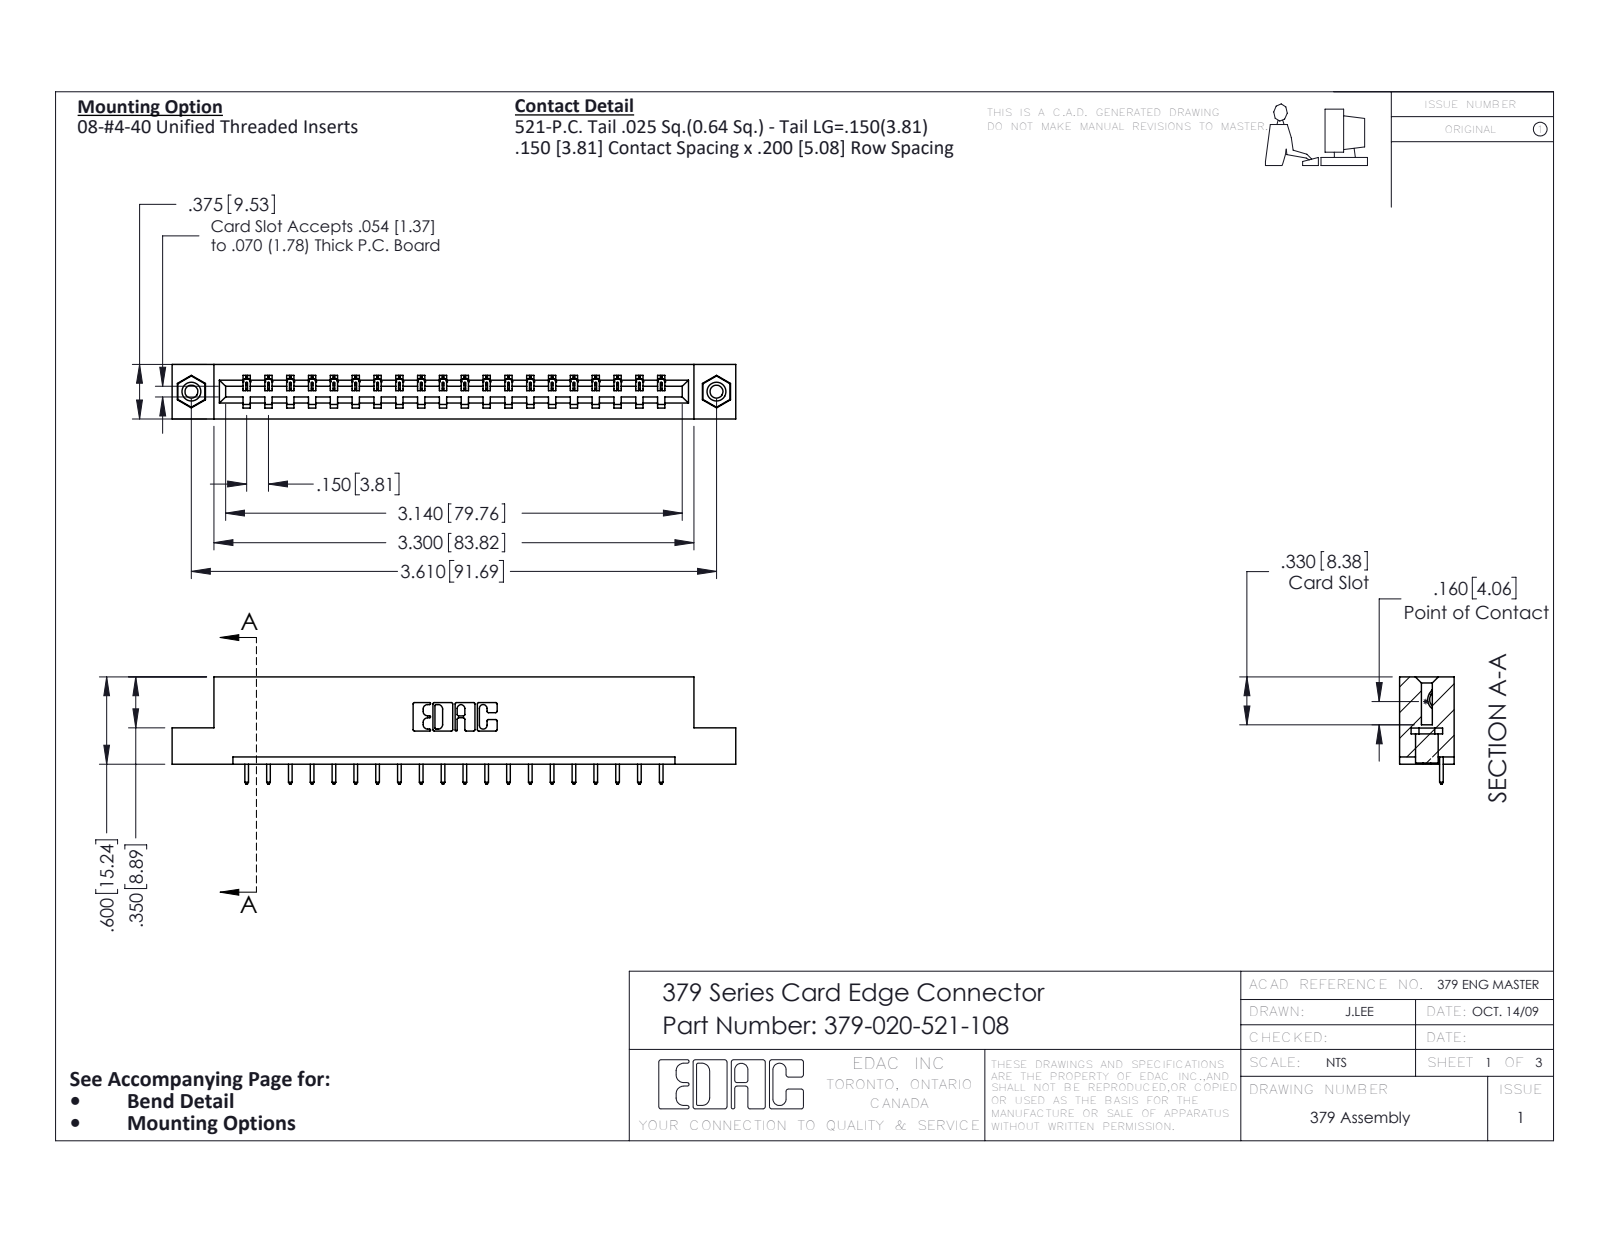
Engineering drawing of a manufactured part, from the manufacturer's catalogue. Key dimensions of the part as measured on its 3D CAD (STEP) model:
Part name (STEP PRODUCT): 345-250-001_345-250-003-102; 345-292-001_345-293-121; 379 Part_Flush - .156 Dia - TI; 379-020-521-108
STEP written by: SolidWorks 2016 (CONFIG_CONTROL_DESIGN)
Units: inches
Bodies: 23 solids, 1334 faces (942 planar, 376 cylindrical, 16 other)
Overall size (bounding box): 3.875 × 0.737 × 0.375
Volume: 0.611 in³ · Surface area: 15.39 in²
Round holes (diameter × count): ⌀0.089 ×2, ⌀0.125 ×2, ⌀0.156 ×2
Round bosses / shafts (diameter × count): ⌀0.155 ×2
Partial cylindrical surfaces — rounded edges, fillets, slot ends (radius × count): R0.006 ×40, R0.01 ×40, R0.01 ×22, R0.007 ×6, R0.031 ×6, R0.026 ×3, R0.014 ×1, R0.022 ×1
Main face-to-face distances: 0.3, 0.075, 0.375, 0.6, 0.225, 0.15, 0.45, 0.2, 0.75, 0.55
Hole centre spacings: 3.61
